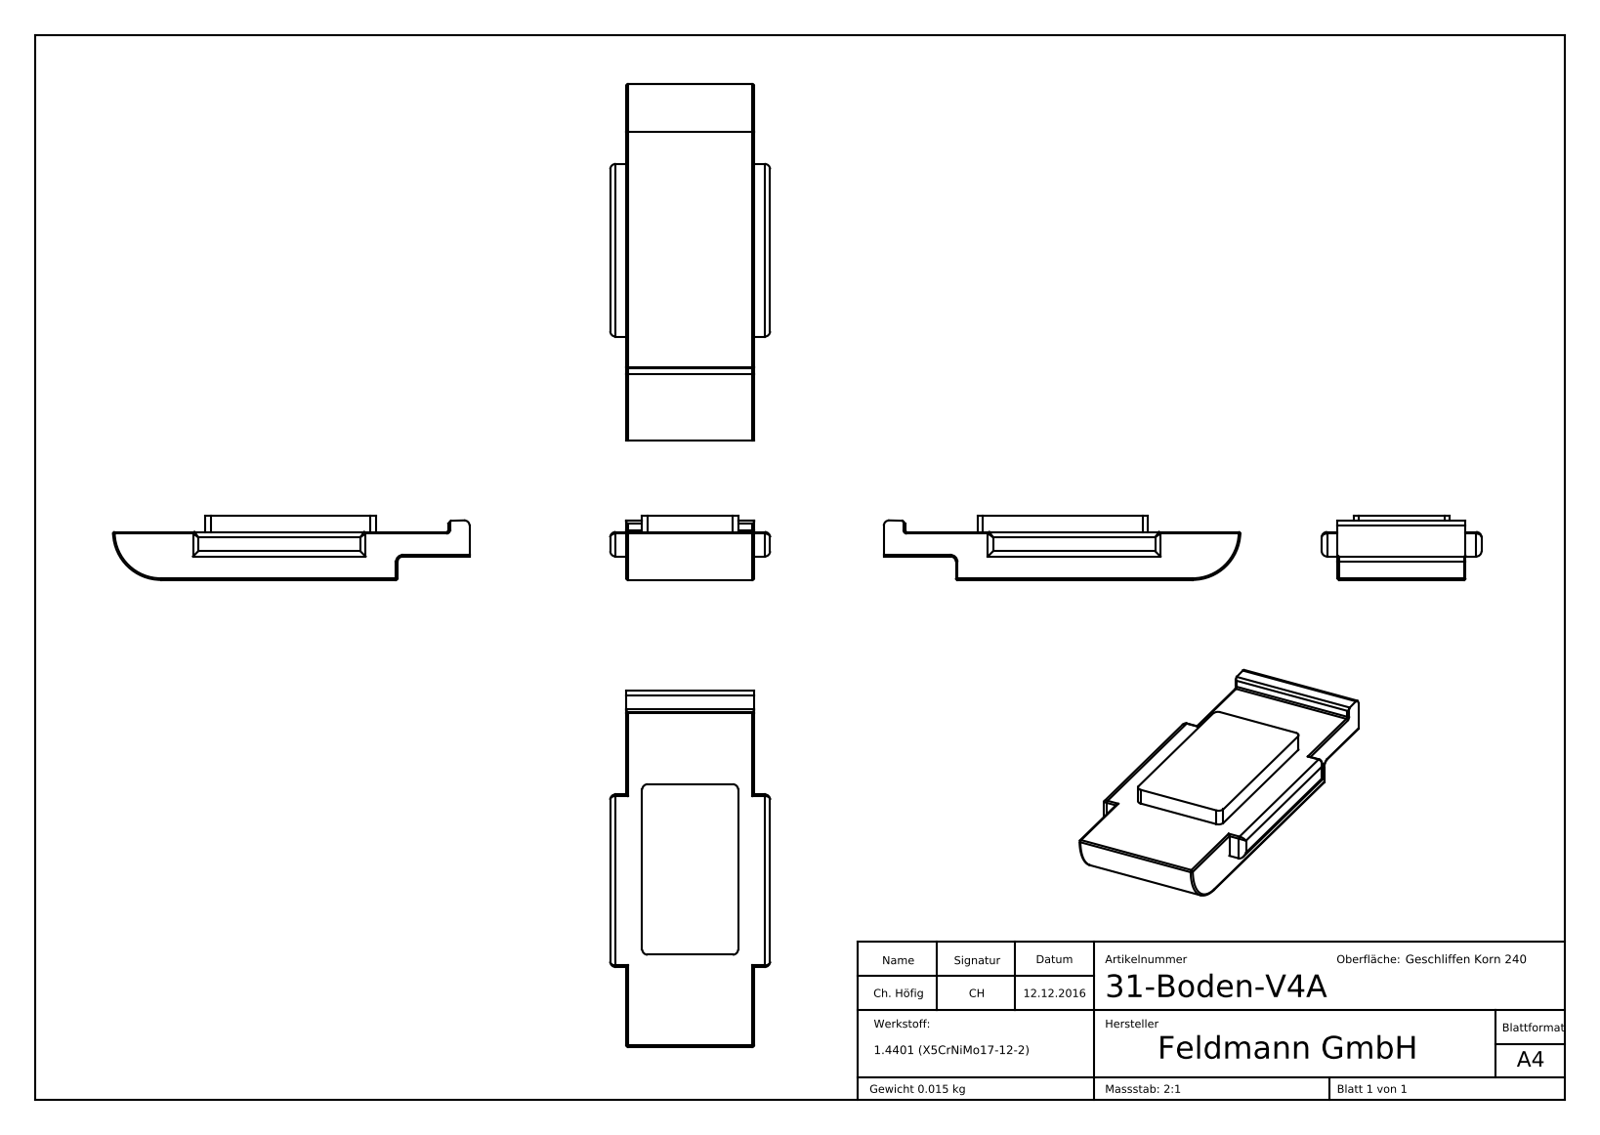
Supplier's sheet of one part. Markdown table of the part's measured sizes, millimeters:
| quantity | value |
| --- | --- |
| part name | 31-BODEN-V4A |
| STEP written by | SolidWorks 2018 (CONFIG_CONTROL_DESIGN) |
| units | millimeters |
| bodies | 1 solid, 71 faces (23 planar, 34 cylindrical, 14 other) |
| overall size | 33.46 × 15 × 6 |
| volume | 1 925 mm³ |
| surface area | 1 332 mm² |
| partial cylindrical surfaces (radius × count) | 0.15 × 15, 0.5 × 14, 4.5 × 1 |
| main face-to-face distances | 4.5, 1.5, 6, 12, 2.2, 2.3, 3.8, 10.5, 3, 13.5 |
